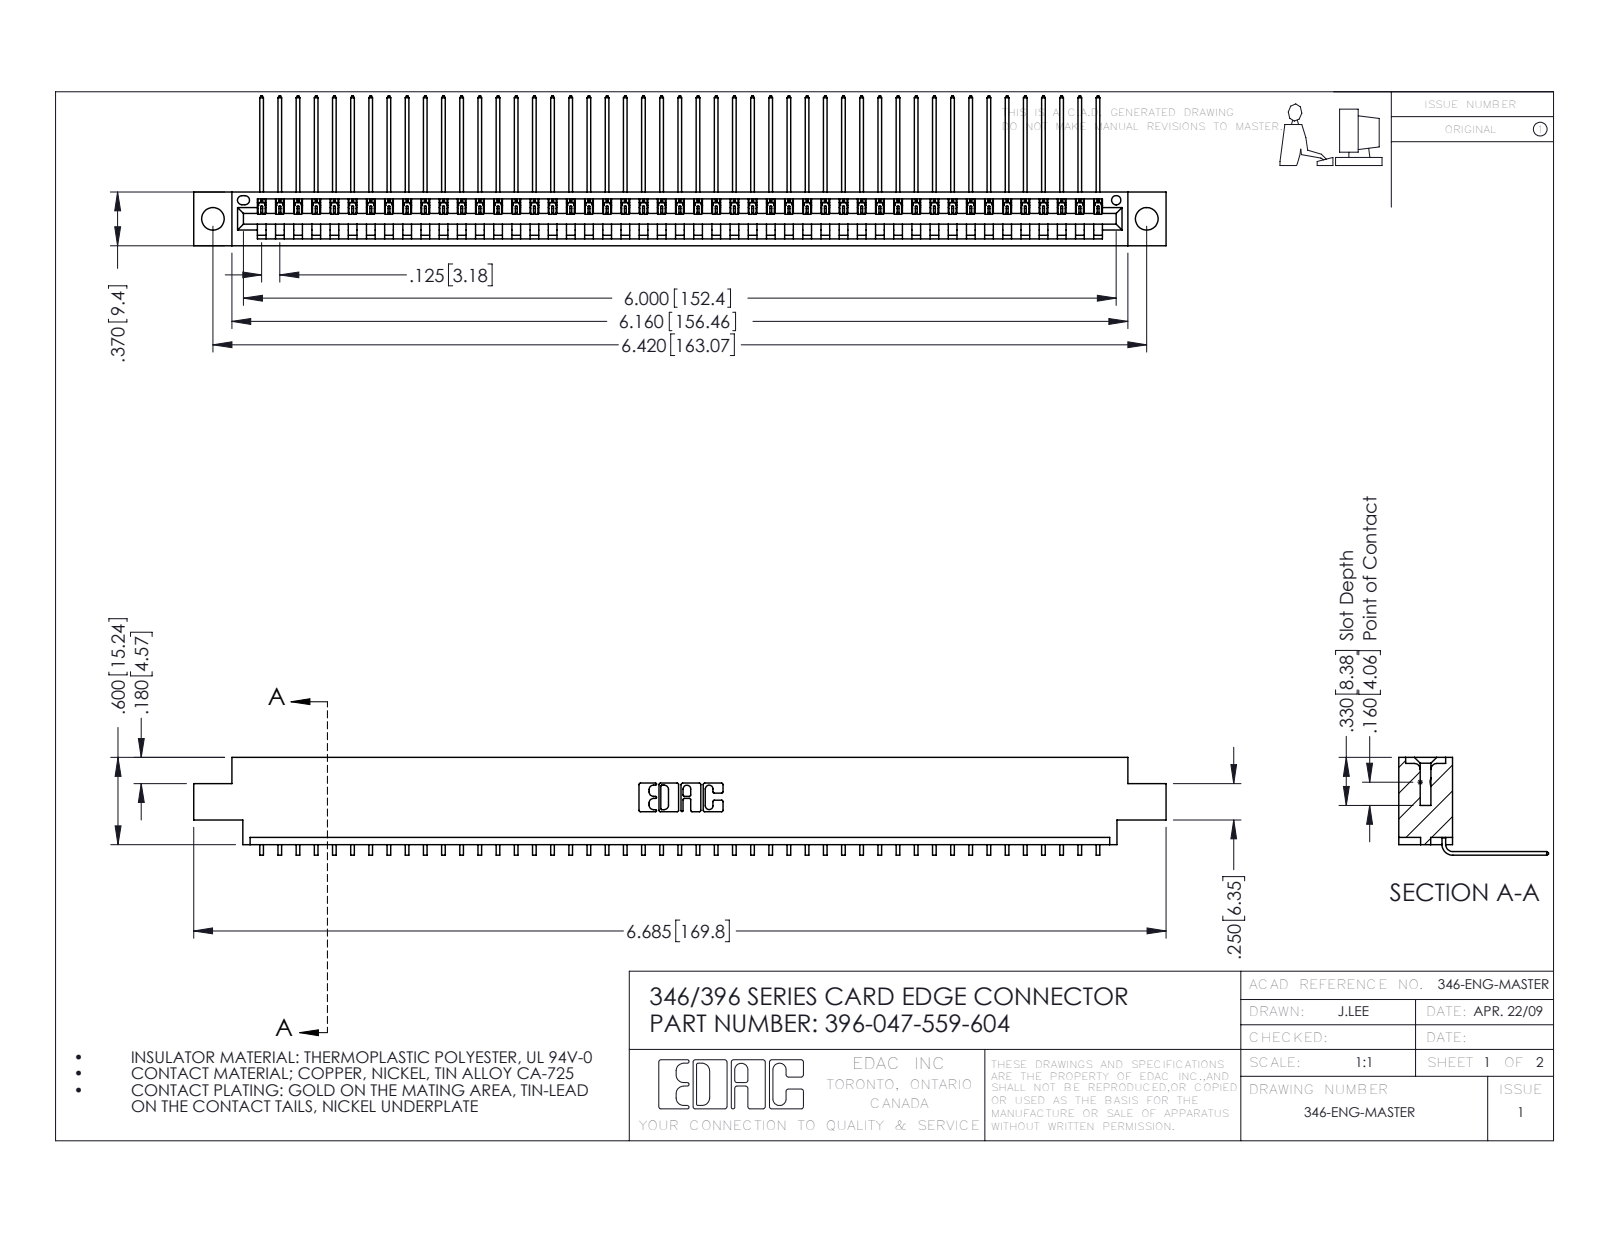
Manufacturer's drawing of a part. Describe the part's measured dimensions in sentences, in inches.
The part is named "346 Part_0.170 Offset - 0.156 Dia-TH; 396-047-559-604; 345-292-001_558 559 Tail - 1". Its 3-D file was written by "SolidWorks 2016 (CONFIG_CONTROL_DESIGN)". It is 48 solids with 2946 faces: 2054 planar, 892 cylindrical and 0 other. Overall it measures 6.685 by 1.03 by 0.673 inches. Its volume is 0.989 cubic inches and its surface area 32.87 square inches. Round holes: 2 of diameter 0.156, 1 of diameter 0.064. Partial cylindrical surfaces (rounded edges, fillets, slot ends): 94 of radius 0.006, 22 of radius 0.01, 6 of radius 0.007, 6 of radius 0.031, 3 of radius 0.026, 2 of radius 0.031, 2 of radius 0.04, 1 of radius 0.014. The main face-to-face distances are 0.048, 0.322, 0.37, 0.025, 0.25, 0.072, 0.298, 0.148, 0.222, 0.1. The hole center spacings are 0.246, 6.211, 6.42.
